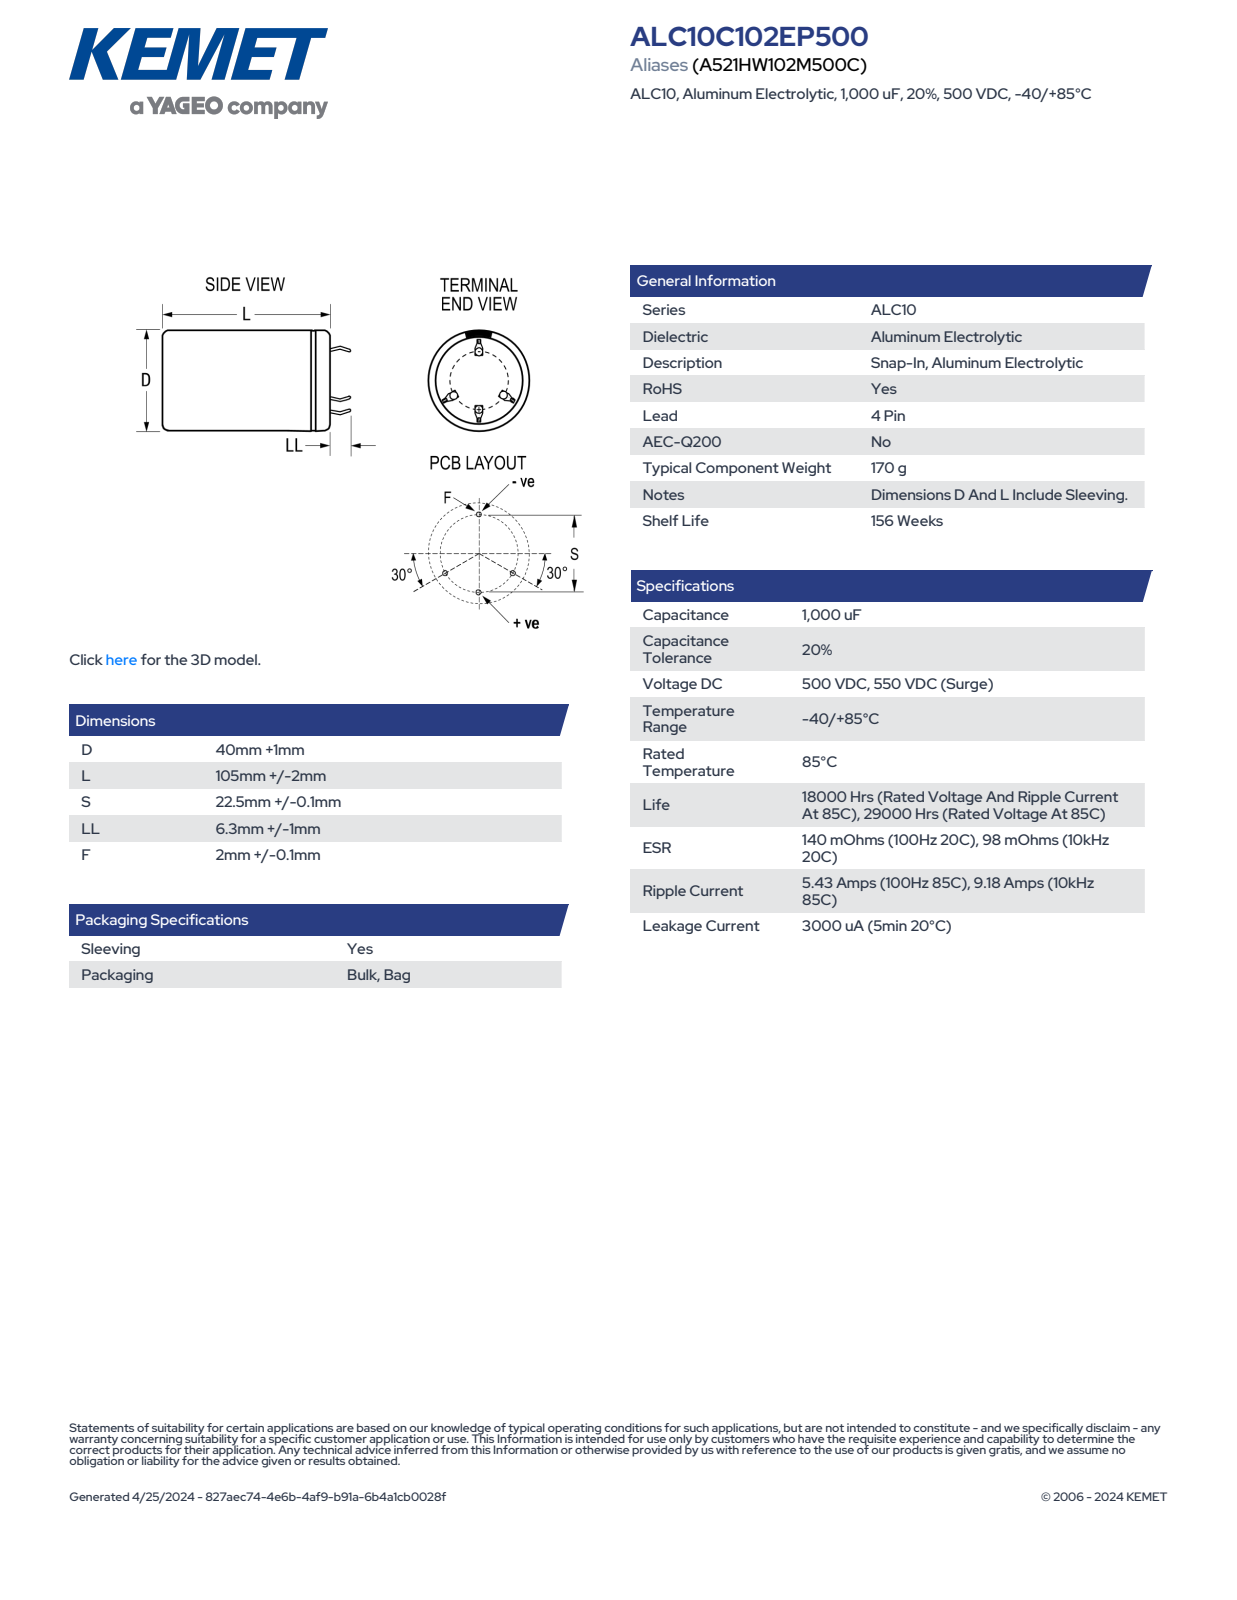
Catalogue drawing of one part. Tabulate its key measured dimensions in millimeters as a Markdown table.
| quantity | value |
| --- | --- |
| part name | CARS_K4P_40X105_D41L107S22.5LL7.3F2.1 |
| STEP written by | SolidWorks 2014 (AUTOMOTIVE_DESIGN) |
| units | millimeters |
| bodies | 1 solid, 134 faces (80 planar, 15 cylindrical, 39 other) |
| overall size | 114.29 × 41 × 41 |
| volume | 140 496 mm³ |
| surface area | 16 477 mm² |
| round holes (diameter × count) | 36.28 × 1 |
| round bosses / shafts (diameter × count) | 41 × 1 |
| partial cylindrical surfaces (radius × count) | 20.49 × 1 |
| main face-to-face distances | 106.99, 107.49, 0.5, 0.33, 0.6, 18.13, 0.75, 1.35, 17.8, 18.46 |
